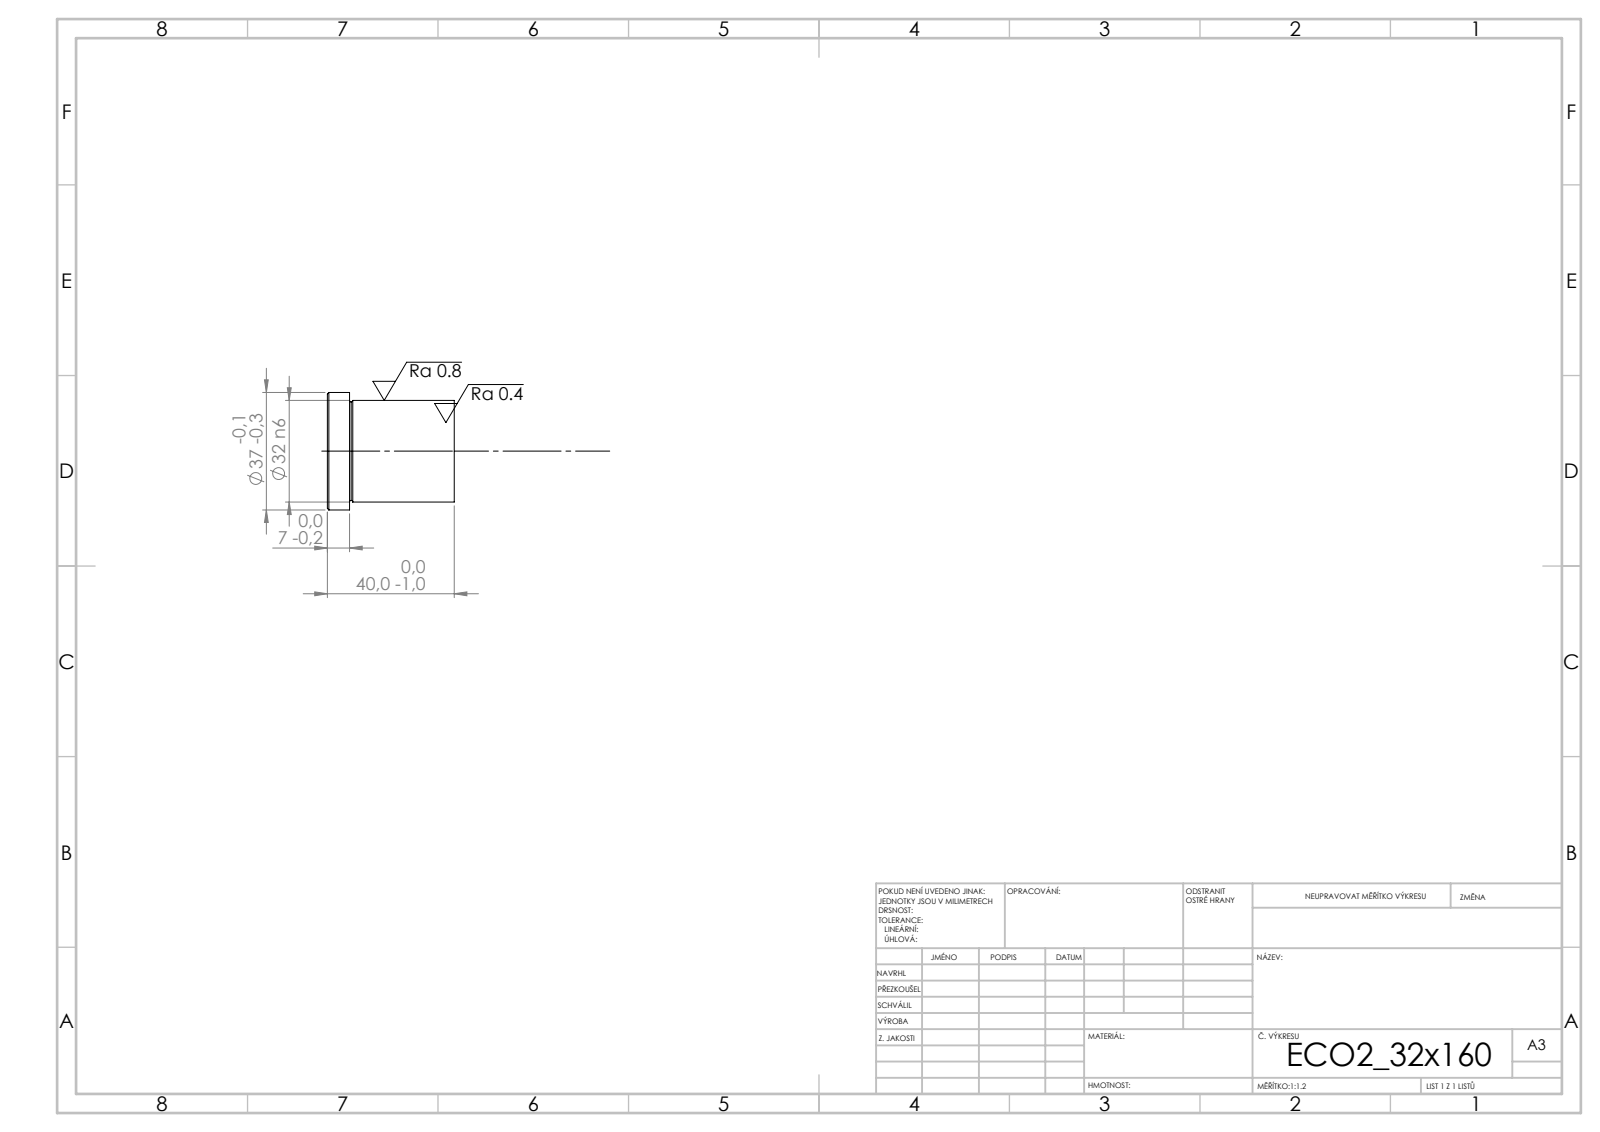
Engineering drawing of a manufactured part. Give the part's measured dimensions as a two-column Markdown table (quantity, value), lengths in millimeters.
| quantity | value |
| --- | --- |
| STEP written by | SolidWorks 2019 (CONFIG_CONTROL_DESIGN) |
| units | millimeters |
| bodies | 1 solid, 13 faces (3 planar, 4 cylindrical, 6 other) |
| overall size | 40 × 37 × 37 |
| volume | 34 013 mm³ |
| surface area | 6 301 mm² |
| round bosses / shafts (diameter × count) | 37 × 1, 32 × 1 |
| main face-to-face distances | 40, 33, 7 |
